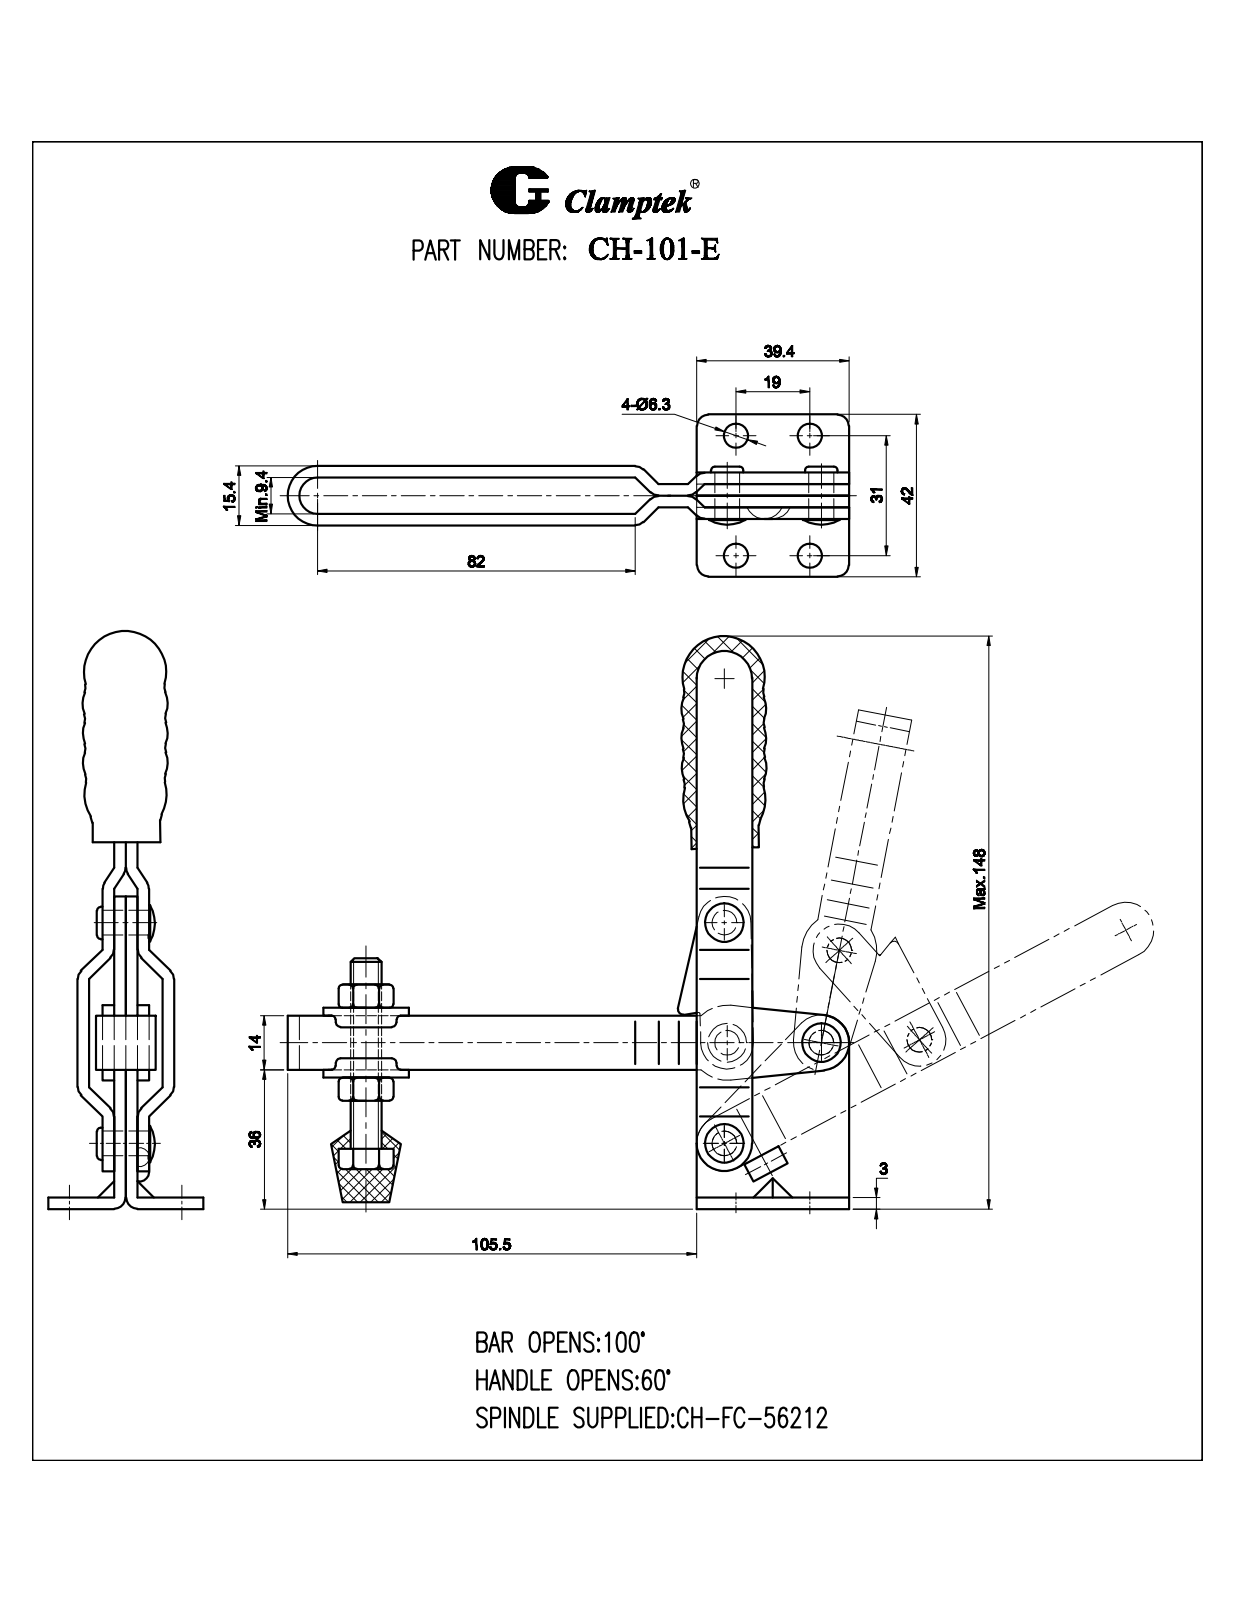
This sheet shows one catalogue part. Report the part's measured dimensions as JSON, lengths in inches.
{"part_name": "CH-FC-56212 SPINDLE SUPPLIED; CH-FW-516; CH-101-E; CH-101-E-02 LONG U-BAR (+6 more)", "step_written_by": "SolidWorks 2010 (CONFIG_CONTROL_DESIGN)", "units": "inches", "bodies": {"solids": 18, "faces": 846, "planar": 313, "cylindrical": 254, "other": 279}, "overall_size": [5.981, 5.721, 1.654], "volume_in3": 4.165, "surface_area_in2": 81.56, "round_holes": [[0.248, 6], [0.228, 4], [0.252, 4], [0.251, 2], [0.319, 2], [0.089, 1], [0.312, 1]], "round_bosses_or_shafts": [[0.821, 1], [0.312, 1], [0.079, 1]], "partial_cylinders_radius": [[0.118, 16], [0.039, 10], [0.118, 8], [0.079, 4], [0.118, 4], [0.283, 3], [0.268, 2], [0.426, 2]], "face_to_face_distances": [0.118, 0.236, 0.067, 0.185, 0.303, 0.421, 0.354, 0.051, 0.256, 0.488], "hole_center_spacings": [1.22, 0.748, 1.431, 0.957, 1.026, 1.42, 1.606, 2.244]}
